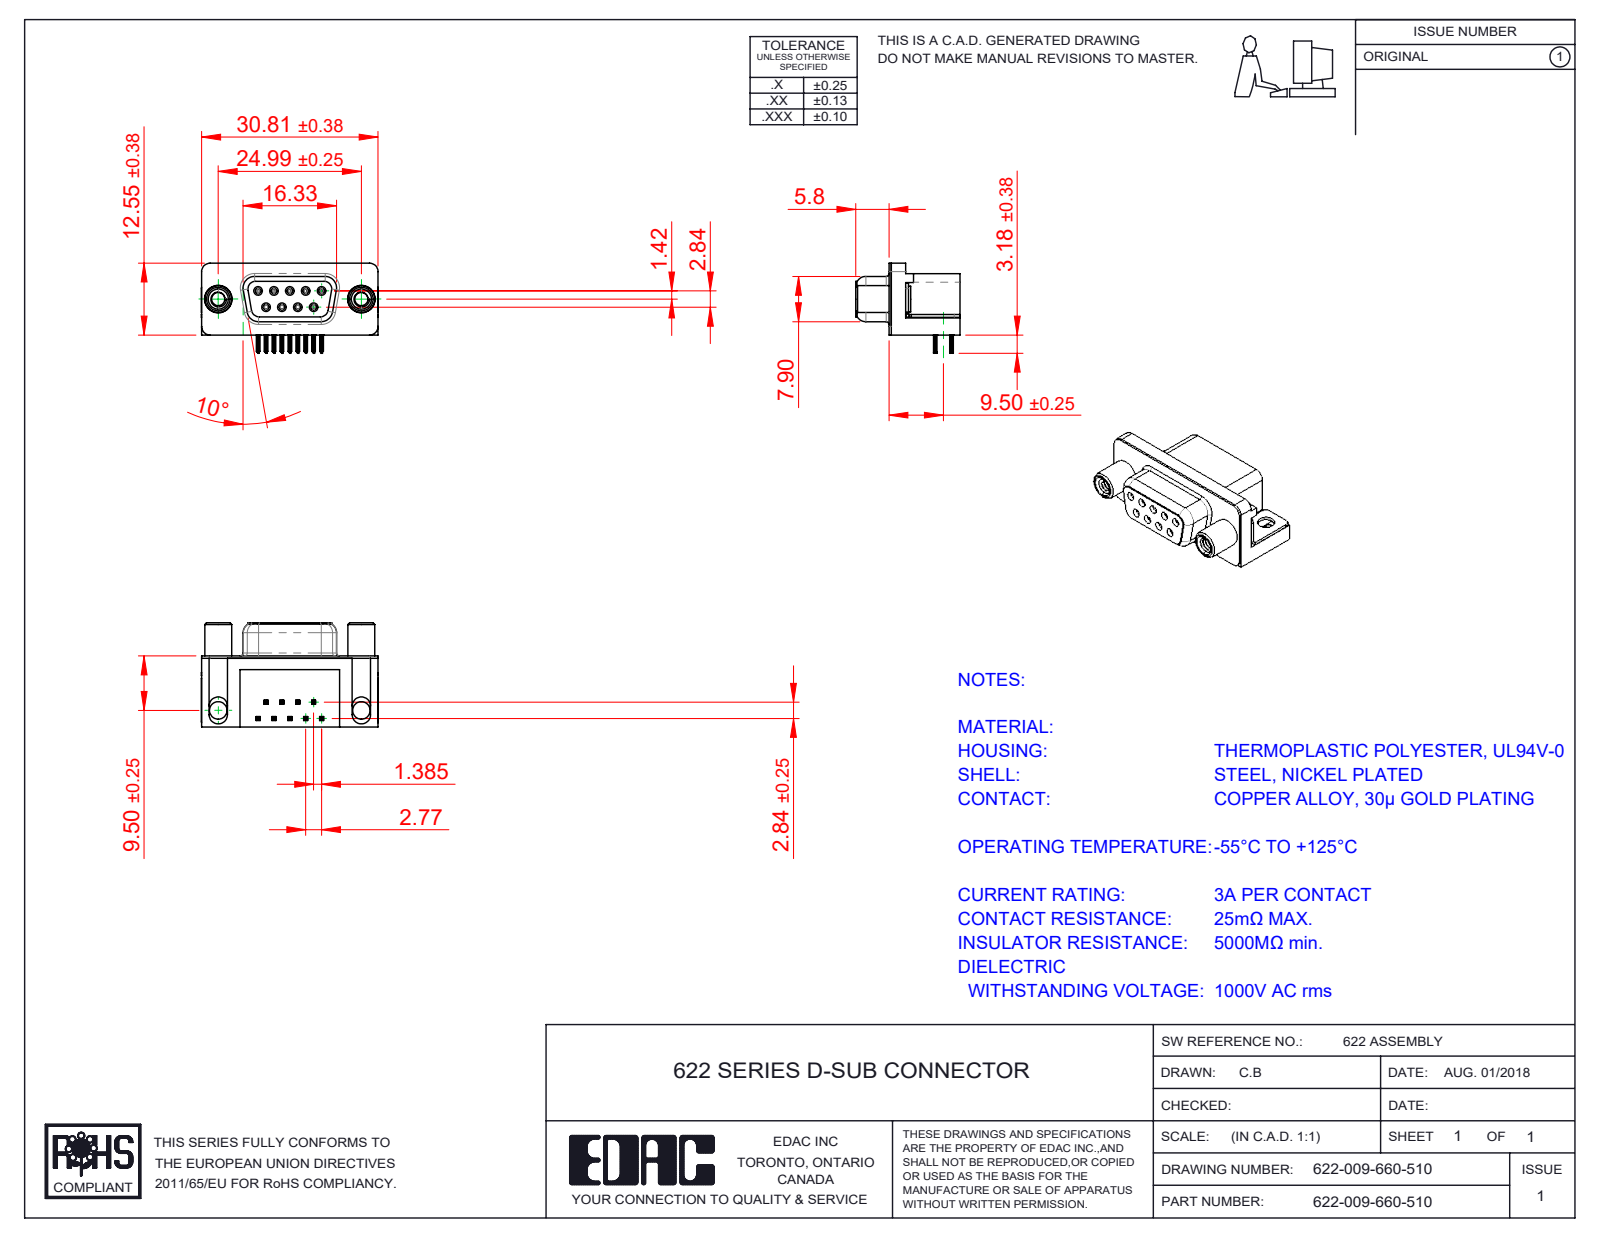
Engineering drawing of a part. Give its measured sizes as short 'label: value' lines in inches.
name: 622 Socket Bottom; 622-009-660-510; 622 Contact Top; 622 Round Threaded Standoff (+3 more)
written by: SolidWorks 2016 (CONFIG_CONTROL_DESIGN)
unit: in
bodies: 15 solids, 1564 faces (674 planar, 424 cylindrical, 466 other)
size: 1.216 × 0.717 × 0.619
volume: 0.233 in³; area: 8.153 in²
holes: 9× ⌀0.031, 9× ⌀0.035, 2× ⌀0.091, 2× ⌀0.12, 2× ⌀0.122, 2× ⌀0.157, 2× ⌀0.189, 2× ⌀0.197
bosses: 9× ⌀0.047, 2× ⌀0.193, 2× ⌀0.185, 2× ⌀0.177, 2× ⌀0.152
rounds: 72× R0.004, 36× R0.006, 18× R0.014, 18× R0.039, 9× R0.013, 8× R0.053, 8× R0.063, 7× R0.059
face distances: 0.016, 0.472, 0.488, 0.014, 0.114, 0.098, 0.407, 0.228, 0.374, 0.244
hole spacings: 0.124, 0.109, 0.218, 0.198, 0.198, 0.327, 0.294, 0.295
